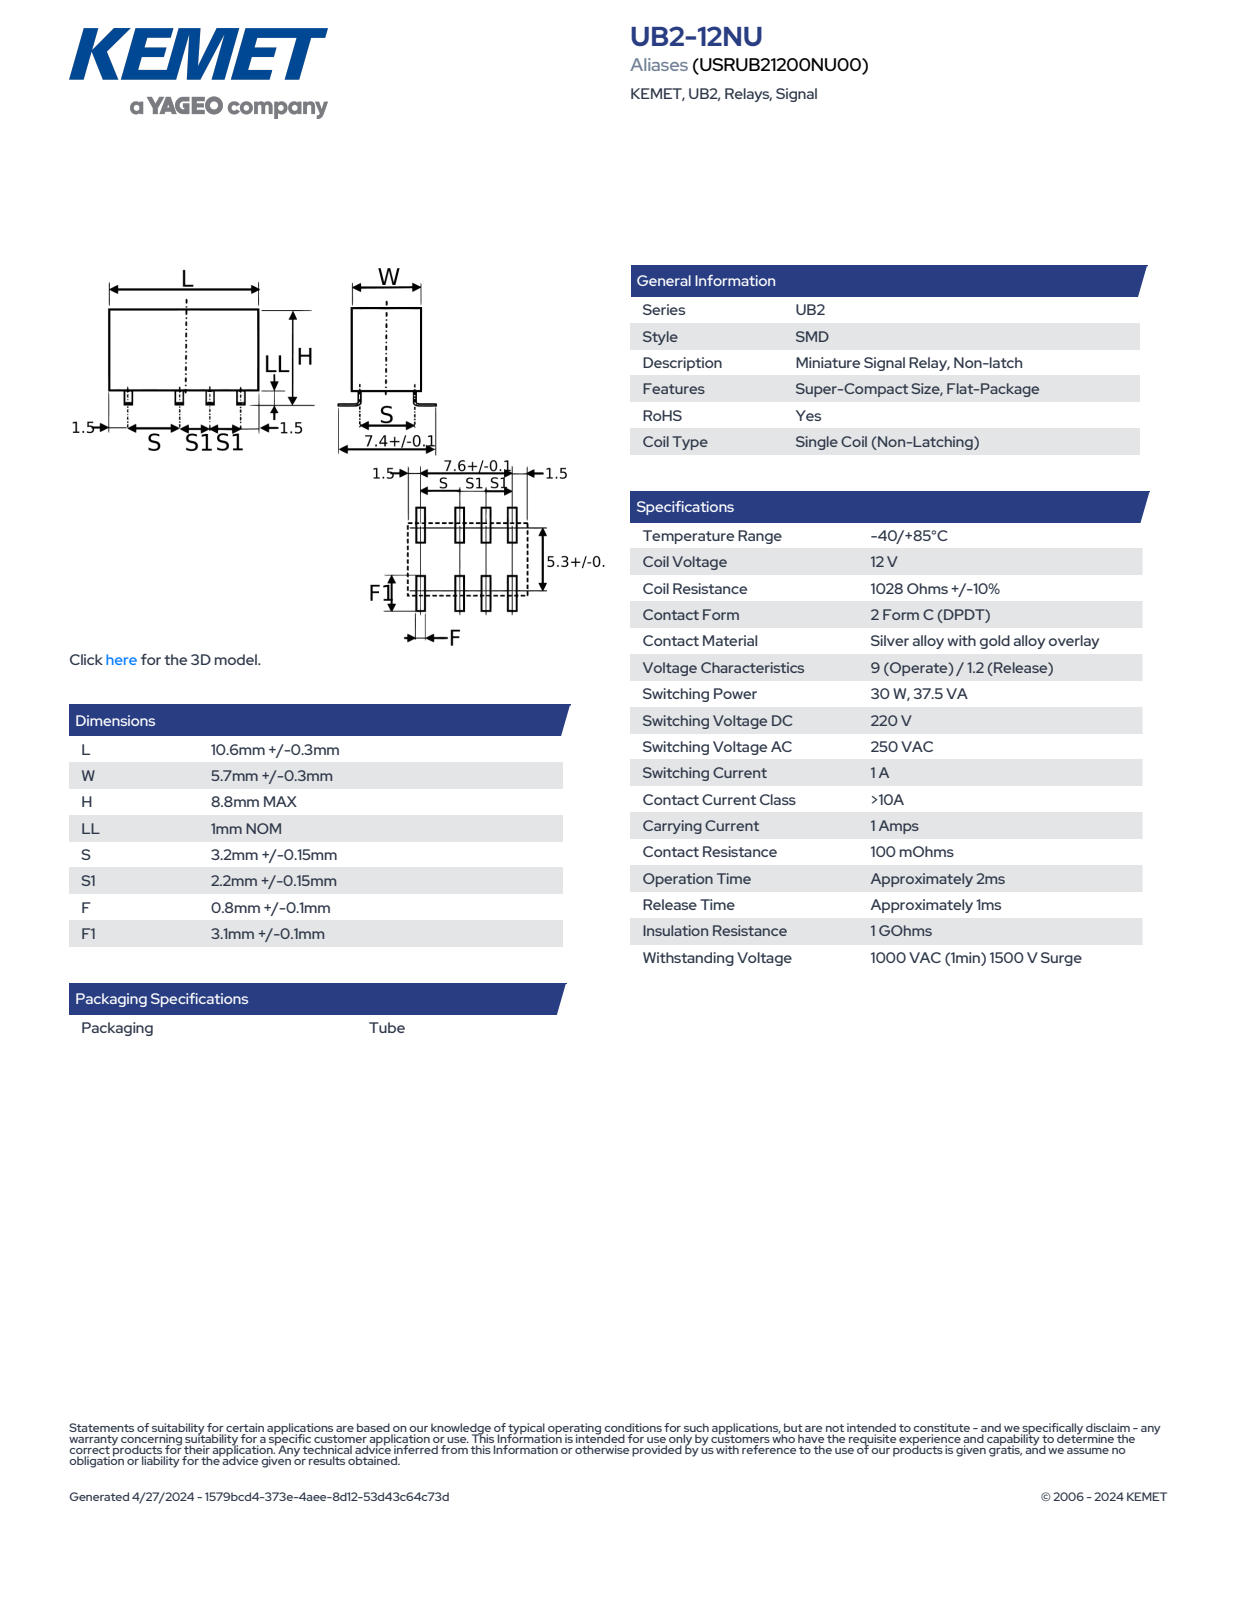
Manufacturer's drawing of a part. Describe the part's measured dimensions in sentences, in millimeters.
The part is named "IR_TUB2S_L10.9W6H8.8". Its 3-D file was written by "SolidWorks 2014 (AUTOMOTIVE_DESIGN)". It is 1 solid with 116 faces: 116 planar, 0 cylindrical and 0 other. Overall it measures 10.9 by 8.8 by 7.4 millimeters. Its volume is 532 cubic millimeters and its surface area 449 square millimeters. The main face-to-face distances are 6, 8.1, 10.9, 0.7, 8.8, 0.6, 8.7, 4.55, 3.2, 1.45.
